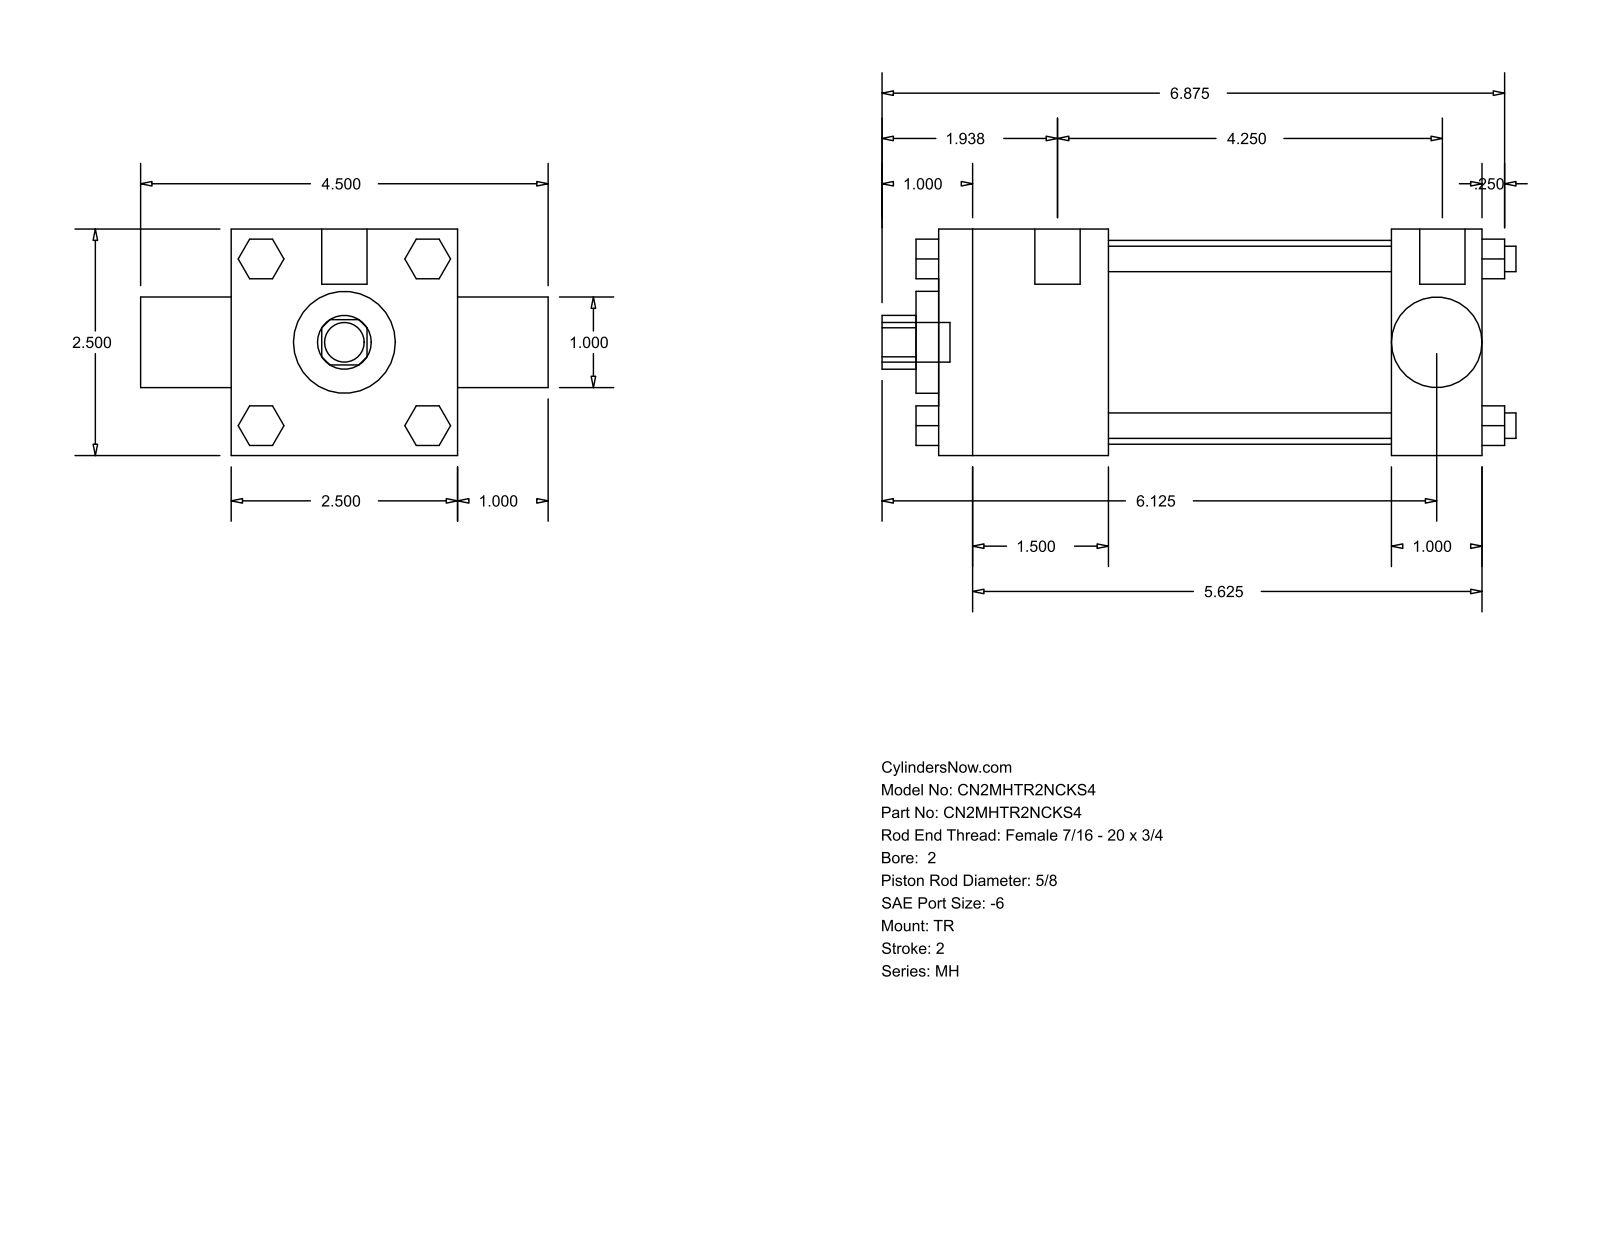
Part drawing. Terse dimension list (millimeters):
name: MH_TR__0200_0.625
written by: GSSL Pune (CONFIG_CONTROL_DESIGN)
unit: mm
bodies: 0 solids, 120 faces (92 planar, 28 cylindrical, 0 other)
size: 177.8 × 114.3 × 63.5
holes: 1× ⌀15.88, 1× ⌀25.35, 1× ⌀28.57, 1× ⌀57.15
bosses: 4× ⌀7.14, 3× ⌀5.56, 2× ⌀12.7, 1× ⌀11.11
rounds: 1× R7.54
face distances: 63.5, 152.4, 25.4, 47.62, 127, 79.38, 104.78, 88.9, 158.75, 6.35
